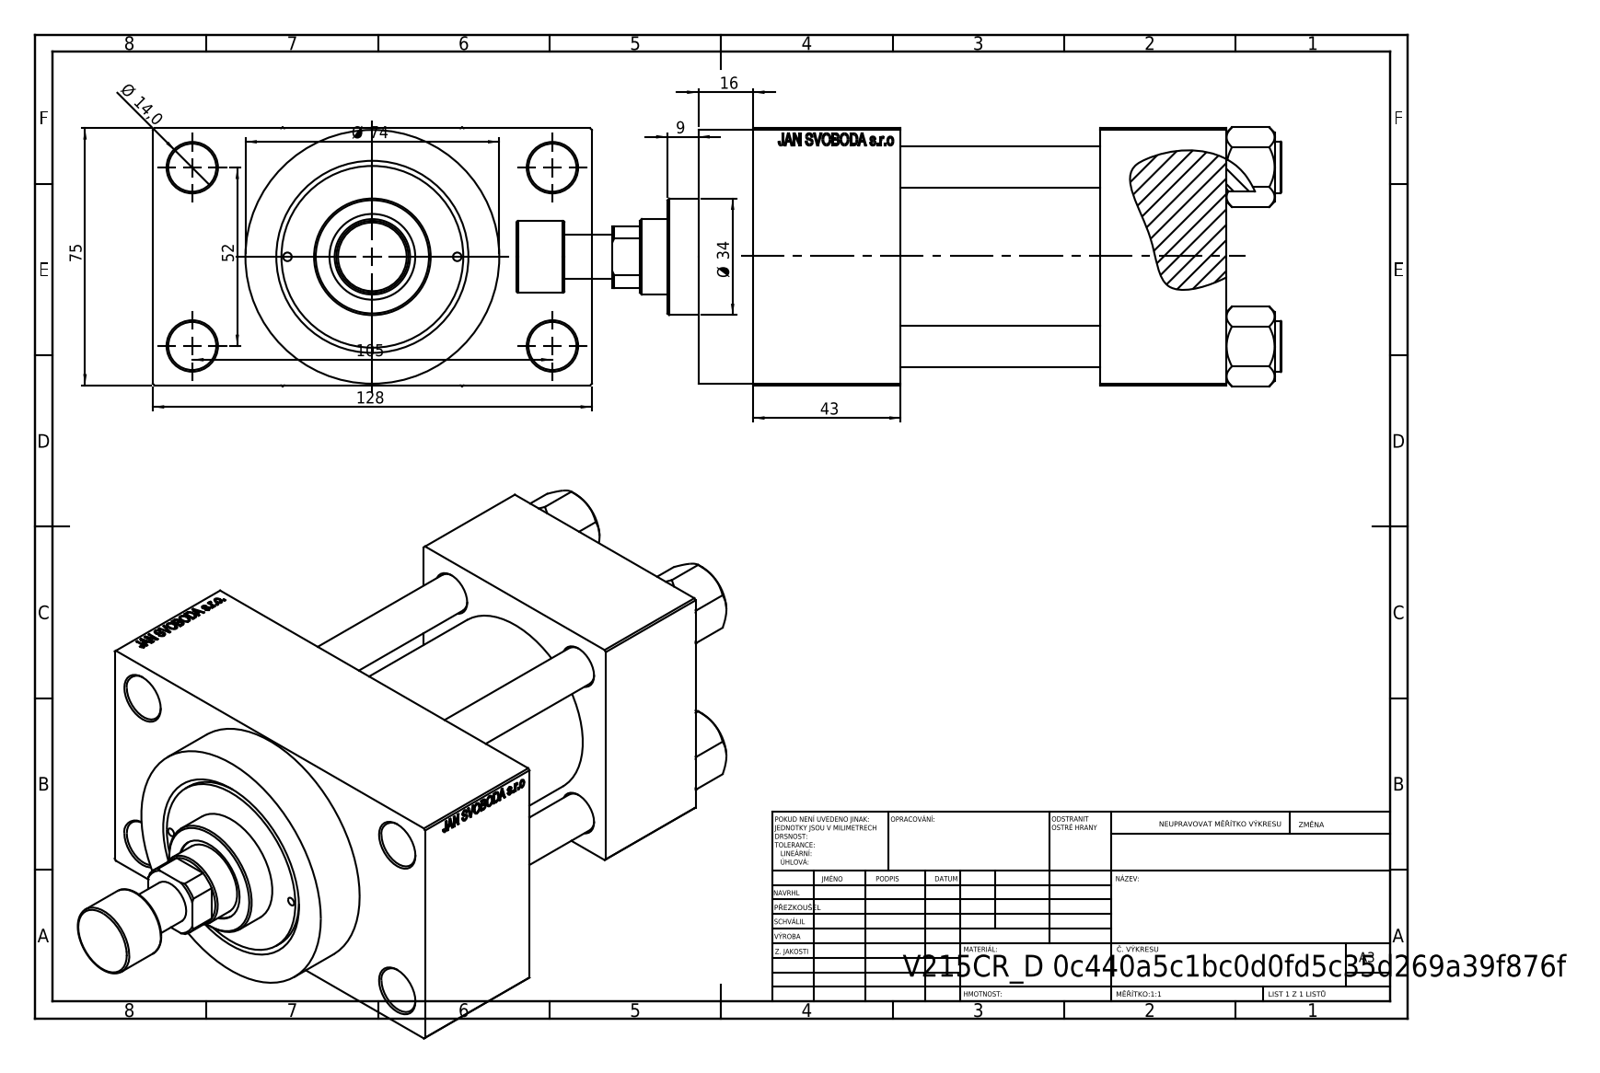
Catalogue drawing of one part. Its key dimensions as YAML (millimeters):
part_name: "V215_VC_A; V215CR_ROD_END_F; V215CR_D_Body; NUT_M5_D (+2 more)"
step_written_by: "SolidWorks 2019 (CONFIG_CONTROL_DESIGN)"
units: millimeters
bodies: {solids: 12, faces: 1122, planar: 502, cylindrical: 96, other: 524}
overall_size: [223, 128, 75.54]
volume: 803978
surface_area: 168782
round_holes:
  - {diameter: 12, count: 4}
  - {diameter: 14, count: 4}
  - {diameter: 2.5, count: 2}
  - {diameter: 7, count: 2}
  - {diameter: 20.96, count: 2}
  - {diameter: 30, count: 2}
  - {diameter: 10.5, count: 1}
  - {diameter: 22, count: 1}
  - {diameter: 25, count: 1}
  - {diameter: 41, count: 1}
  - {diameter: 50, count: 1}
  - {diameter: 53, count: 1}
round_bosses_or_shafts:
  - {diameter: 15, count: 4}
  - {diameter: 74, count: 1}
  - {diameter: 56, count: 1}
  - {diameter: 34, count: 1}
  - {diameter: 21, count: 1}
  - {diameter: 13, count: 1}
face_to_face_distances: [75, 58, 37, 95, 26.5, 138, 101, 43, 101.5, 16]
hole_center_spacings: [26.19, 26.35, 36.98, 38.03, 52.3, 57.22, 58.43, 58.59]
